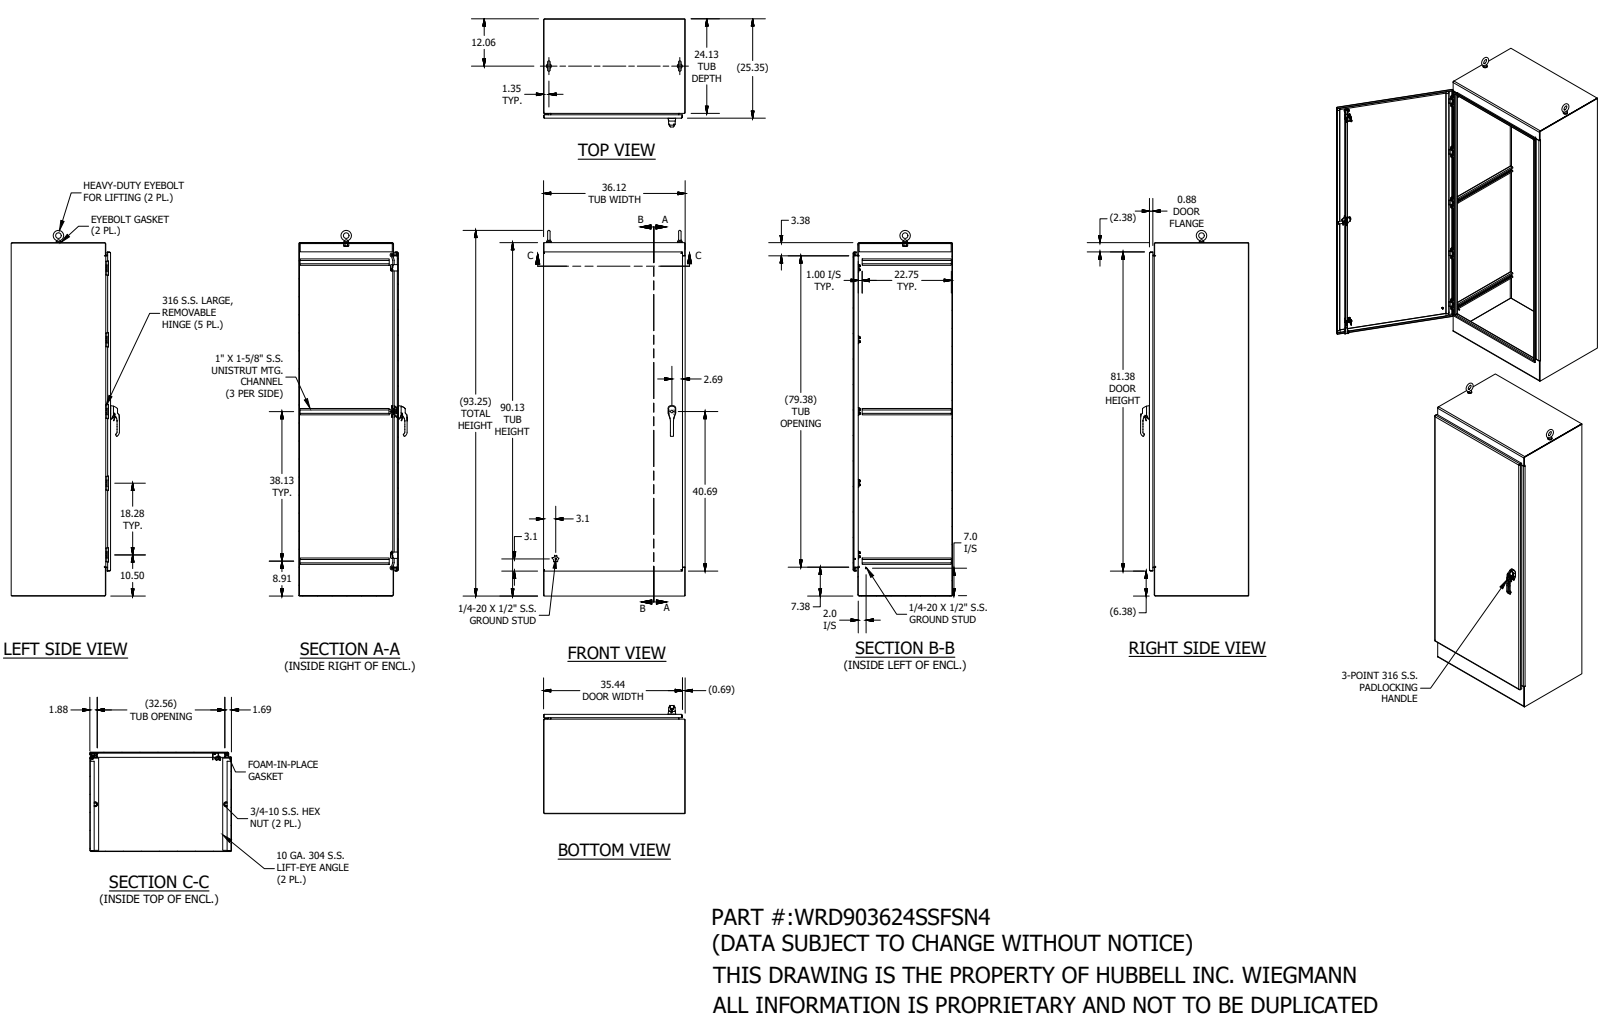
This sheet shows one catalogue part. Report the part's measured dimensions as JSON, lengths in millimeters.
{"part_name": "WRD903624SSFSN4", "step_written_by": "SolidWorks 2019 (AUTOMOTIVE_DESIGN)", "units": "millimeters", "bodies": {"solids": 112, "faces": 4027, "planar": 1650, "cylindrical": 1411, "other": 966}, "overall_size": [2368.5, 917.7, 701], "volume_mm3": 25580000, "surface_area_mm2": 18860000, "round_holes": [[3.6, 24], [5, 10], [6.8, 10], [7.5, 10], [16.5, 10], [6.7, 8], [3.5, 4], [4.2, 4], [4.7, 4], [5.1, 4], [5.4, 3], [7.1, 3]], "round_bosses_or_shafts": [[15.9, 10], [6.4, 8], [6, 4], [6, 3], [31.8, 2], [28.4, 2], [25.4, 2], [19.1, 2]], "partial_cylinders_radius": [[0.5, 172], [0.3, 114], [3.2, 36], [1.6, 22], [0.5, 21], [1.6, 16], [1.3, 14], [2, 14]], "face_to_face_distances": [2.6, 914.9, 641.2, 638.6, 643.9, 641.2, 2.6, 912.3, 917.6, 2286.5], "hole_center_spacings": [0.5, 0.4, 0.6, 25.4, 9.7, 19.3, 464.3, 464.3]}
